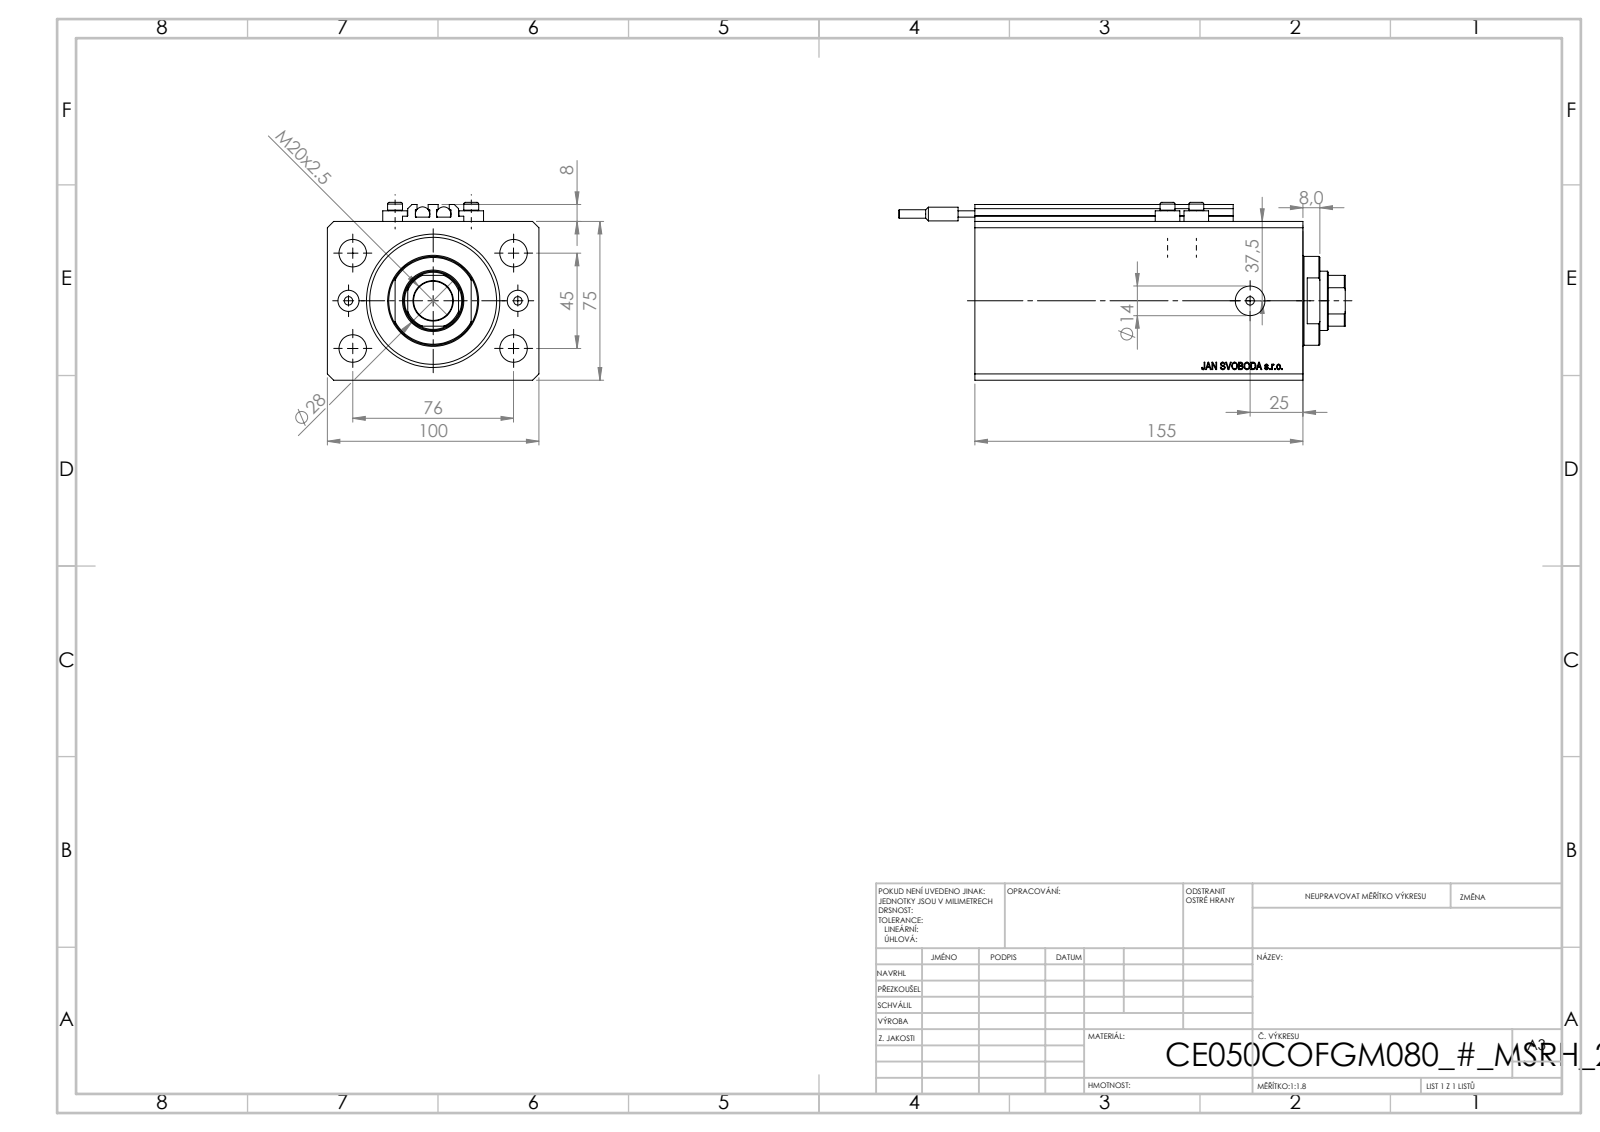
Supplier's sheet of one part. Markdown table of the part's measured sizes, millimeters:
| quantity | value |
| --- | --- |
| part name | V250CE_VC_C; V250CE_C_VCP; SWITCH_V250CE; V250CE_C_Body (+1 more) |
| STEP written by | SolidWorks 2019 (CONFIG_CONTROL_DESIGN) |
| units | millimeters |
| bodies | 10 solids, 1086 faces (536 planar, 98 cylindrical, 452 other) |
| overall size | 211 × 100 × 84 |
| volume | 995 468 mm³ |
| surface area | 170 859 mm² |
| round holes (diameter × count) | 4 × 8, 13 × 4, 10 × 2, 14 × 2, 18.5 × 1, 28 × 1, 50 × 1, 63 × 1 |
| round bosses / shafts (diameter × count) | 11.6 × 4, 7 × 4, 6.8 × 2, 6.5 × 2, 4 × 2, 42 × 1 |
| partial cylindrical surfaces (radius × count) | 0.2 × 10, 13.5 × 1 |
| main face-to-face distances | 75, 100, 155, 20, 11.9, 143.1, 135, 123.1, 80, 2 |
| hole center spacings | 22.59, 44.16, 81.18, 13.6, 36, 38.48, 40, 45 |
